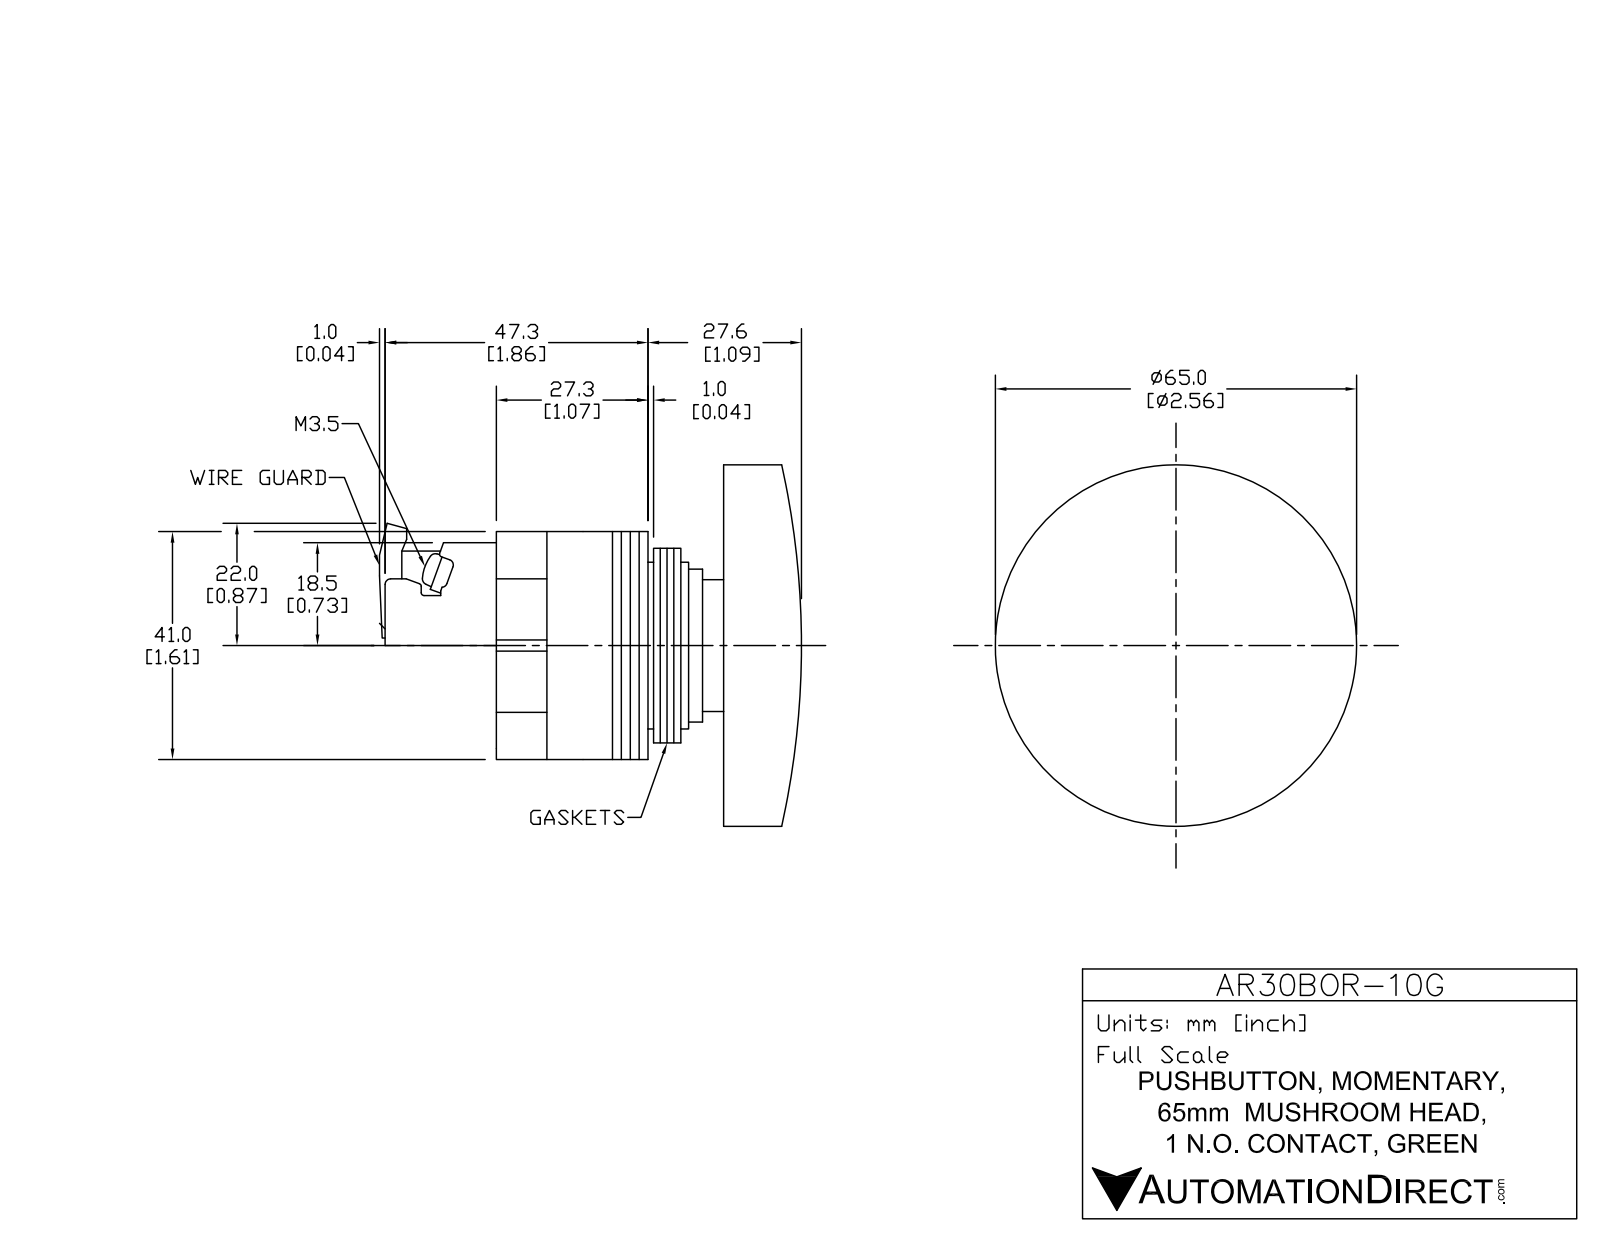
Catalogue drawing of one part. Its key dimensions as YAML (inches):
part_name: "AR30B0R-10G"
step_written_by: "SolidWorks 2017 (AUTOMOTIVE_DESIGN)"
units: inches
bodies: {solids: 14, faces: 246, planar: 140, cylindrical: 92, other: 14}
overall_size: [2.992, 2.559, 2.559]
volume: 4.519
surface_area: 58.25
round_holes:
  - {diameter: 0.118, count: 4}
  - {diameter: 0.945, count: 1}
  - {diameter: 1.181, count: 1}
  - {diameter: 2.362, count: 1}
round_bosses_or_shafts:
  - {diameter: 0.197, count: 2}
  - {diameter: 2.559, count: 1}
  - {diameter: 1.575, count: 1}
  - {diameter: 1.378, count: 1}
  - {diameter: 1.173, count: 1}
partial_cylinders:
  - {radius: 0.197, count: 10}
  - {radius: 0.02, count: 8}
  - {radius: 0.069, count: 4}
  - {radius: 0.118, count: 4}
  - {radius: 0.079, count: 2}
face_to_face_distances: [0.063, 0.126, 0.63, 0.827, 0.197, 1.614, 0.189, 0.63, 0.197, 0.984]
hole_center_spacings: [0.863, 1.22, 1.726]
